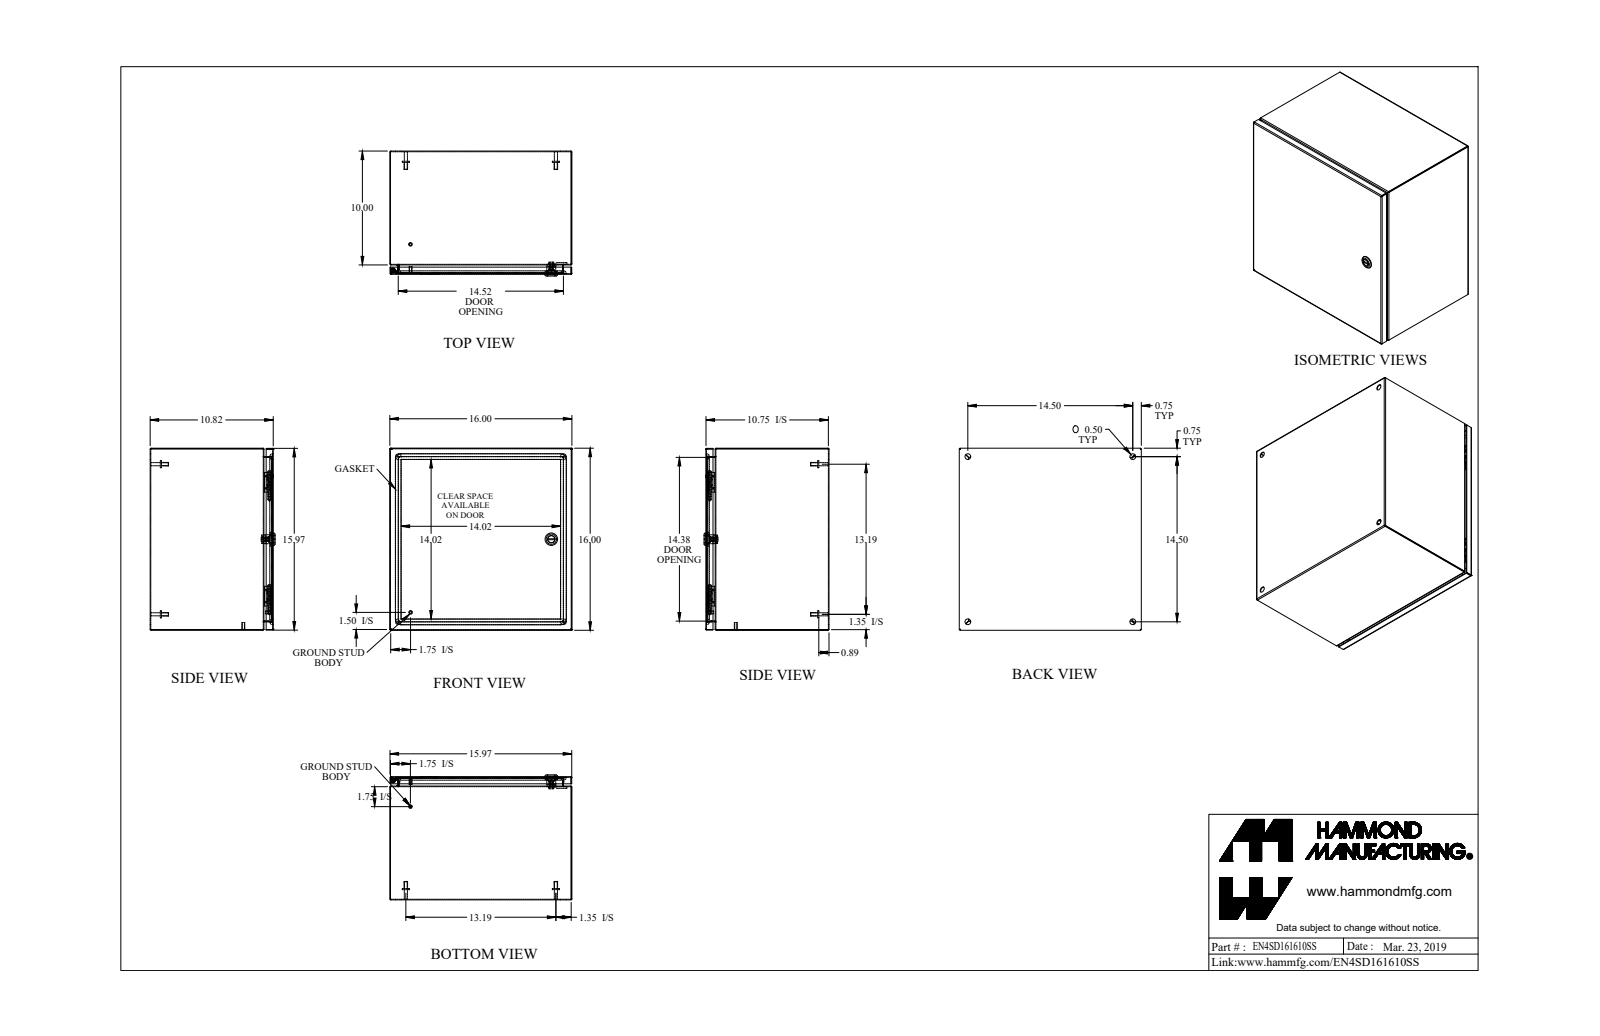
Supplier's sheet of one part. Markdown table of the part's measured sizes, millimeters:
| quantity | value |
| --- | --- |
| part name | EN4SD161610SS_Default |
| STEP written by | SolidWorks 2019 (CONFIG_CONTROL_DESIGN) |
| units | millimeters |
| bodies | 22 solids, 657 faces (303 planar, 212 cylindrical, 142 other) |
| overall size | 406.4 × 406.4 × 278.9 |
| volume | 1 297 000 mm³ |
| surface area | 1 741 000 mm² |
| round holes (diameter × count) | 12.7 × 5, 4.4 × 1, 5 × 1, 6.1 × 1, 6.1 × 1, 9.8 × 1, 16 × 1, 19.5 × 1 |
| round bosses / shafts (diameter × count) | 8 × 6, 15.9 × 4, 7 × 4, 6.4 × 2, 27.9 × 1, 19.9 × 1, 15.9 × 1, 13.3 × 1 |
| partial cylindrical surfaces (radius × count) | 0.7 × 21, 2.2 × 21, 4.8 × 12, 0.2 × 4, 1.6 × 4, 6.4 × 4, 12.7 × 4, 3.2 × 2 |
| main face-to-face distances | 1.4, 405, 273.4, 403.5, 406.4, 272, 274.9, 20.9, 252.6, 19 |
| hole center spacings | 368.3, 186.1, 387.9, 520.9 |
